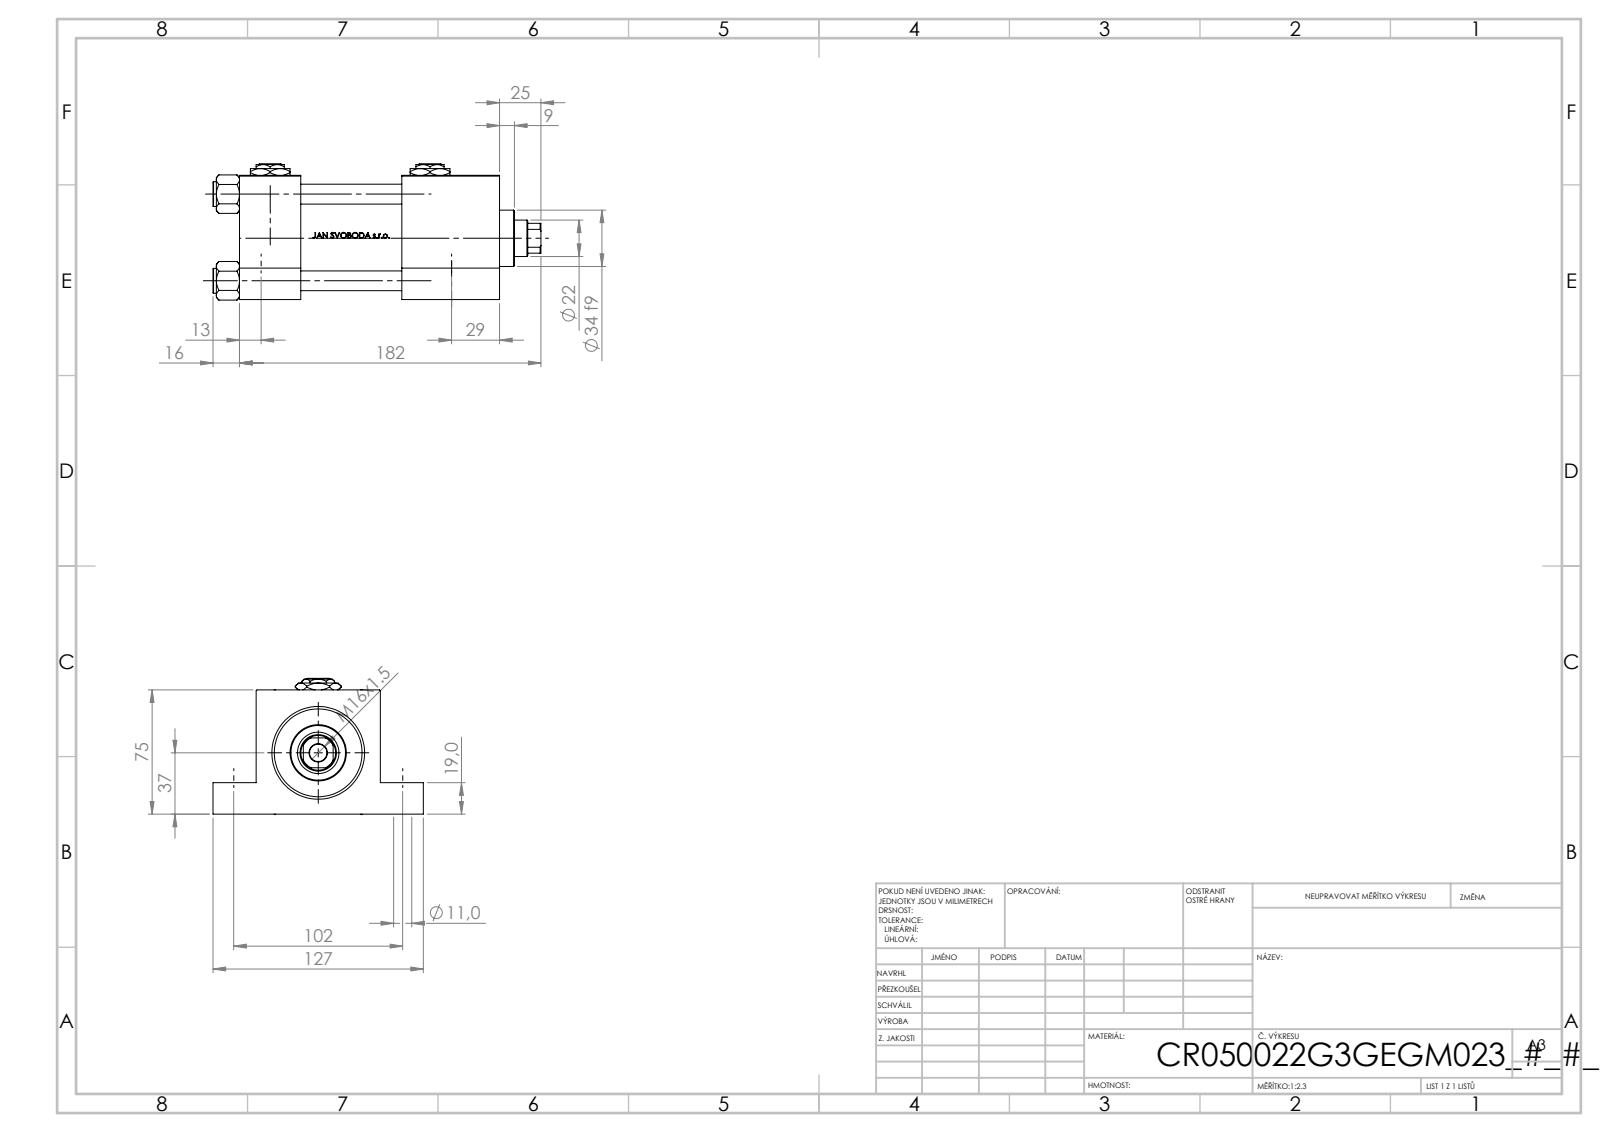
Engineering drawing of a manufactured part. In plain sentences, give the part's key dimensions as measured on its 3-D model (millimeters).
The part is named "V215CR_G_TYCINKA; V215_VC_A; NUT_M5_G; V215CR_VCP_G (+2 more)". Its 3-D file was written by "SolidWorks 2019 (CONFIG_CONTROL_DESIGN)". It is 17 solids with 1252 faces: 496 planar, 136 cylindrical and 620 other. Overall it measures 198 by 127 by 82.27 millimeters. Its volume is 796 460 cubic millimeters and its surface area 178 260 square millimeters. Round holes: 4 of diameter 12, 4 of diameter 14, 2 of diameter 7, 2 of diameter 20.96, 2 of diameter 30, 1 of diameter 10.5, 1 of diameter 22, 1 of diameter 25, 1 of diameter 41, 1 of diameter 50, 1 of diameter 53. Round bosses or shafts: 4 of diameter 15, 1 of diameter 56, 1 of diameter 34. Partial cylindrical surfaces (rounded edges, fillets, slot ends): 1 of radius 10.5. The main face-to-face distances are 75, 37, 157, 120, 19, 98, 56, 61, 59, 26. The hole center spacings are 36.98, 52.3, 51.3, 52.63, 73.96, 102, 114.04, 115.
